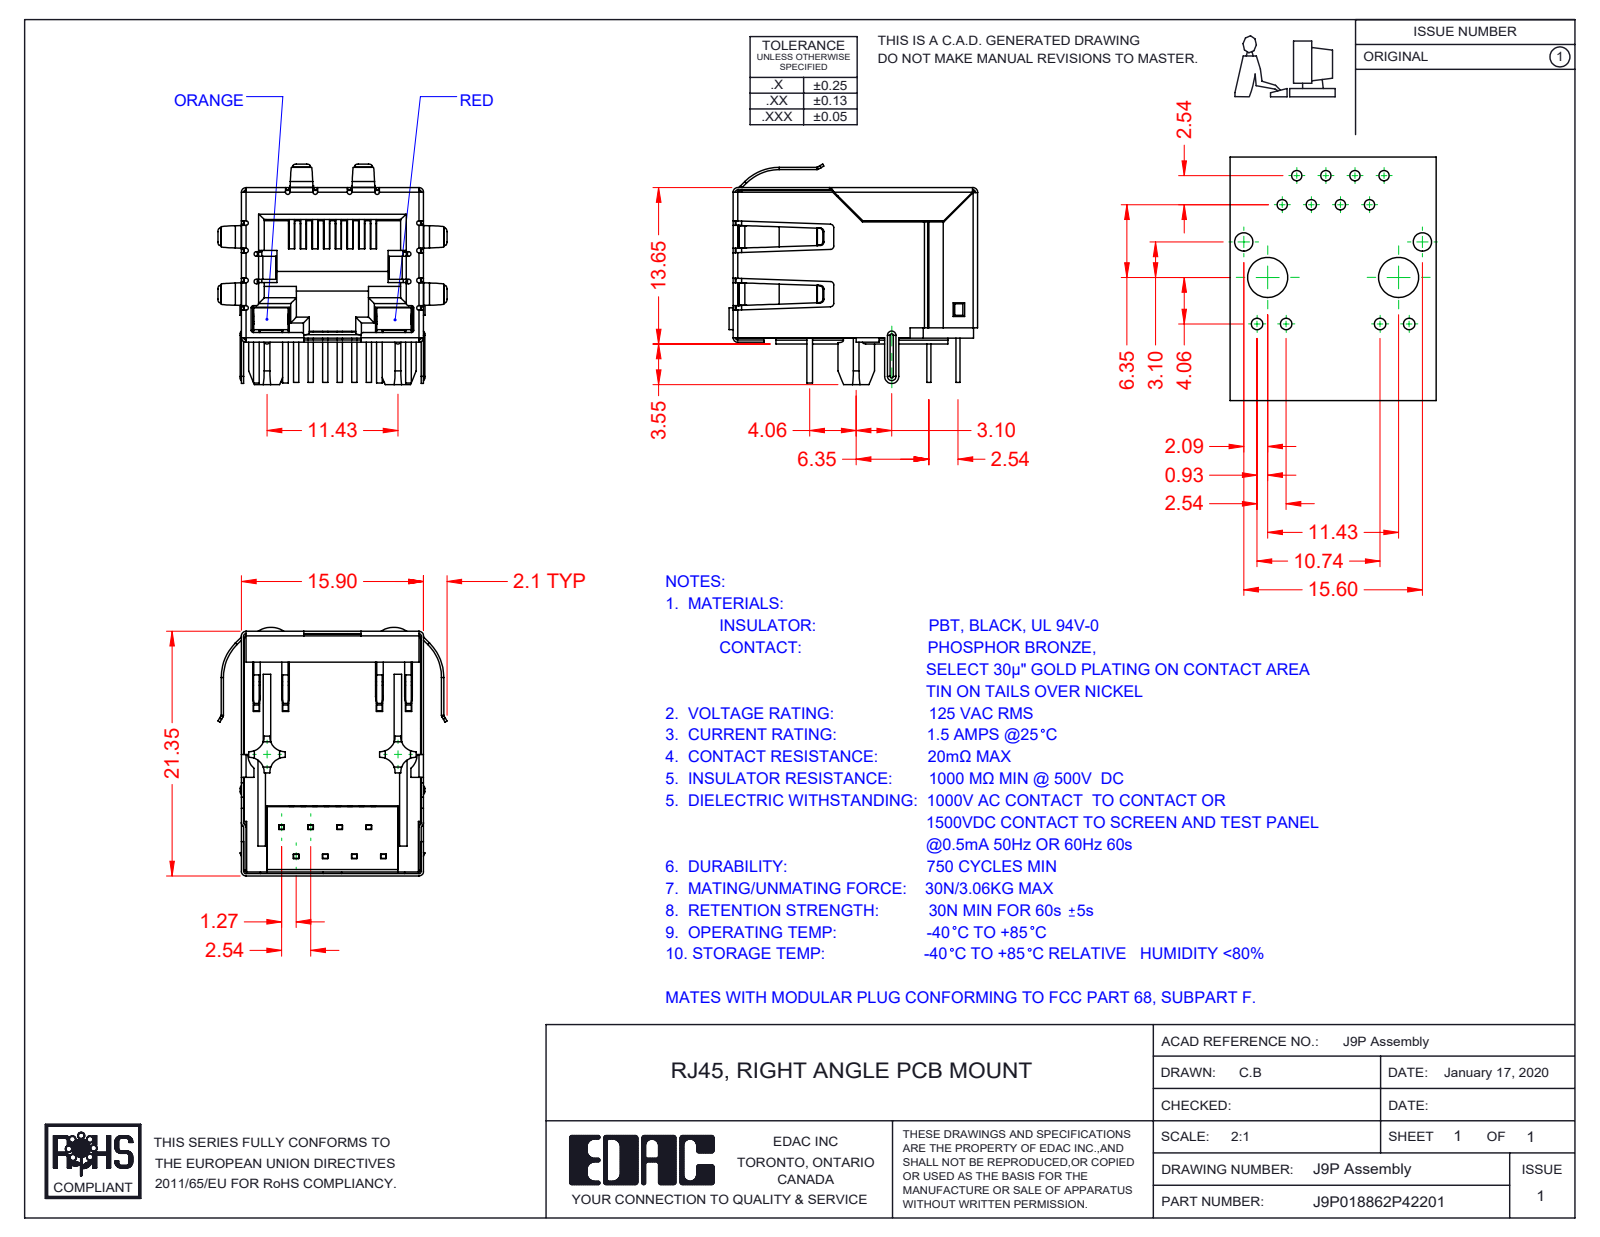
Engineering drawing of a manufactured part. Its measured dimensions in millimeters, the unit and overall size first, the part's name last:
Units: millimetres
Overall size (bounding box): 21.7 × 20 × 19.25
Partial cylindrical surfaces — rounded edges, fillets, slot ends (radius × count): R0.2 ×39, R0.5 ×22, R0.3 ×20, R0.4 ×16, R1.3 ×8, R0.23 ×5, R0.11 ×4, R0.31 ×4
Main face-to-face distances: 15.45, 15.7, 15.65, 0.35, 0.54, 15.5, 12.36, 0.6, 1.4, 0.59
Volume: 2 687 mm³ · Surface area: 7 515 mm²
Bodies: 13 solids, 1472 faces (1042 planar, 336 cylindrical, 94 other)
Part name (STEP PRODUCT): 9P-LED Contact Lock; 9P-LED Contacts; 9P-LED Insulator; 9P-LED Shield (+4 more)
STEP written by: SolidWorks 2016 (CONFIG_CONTROL_DESIGN)
